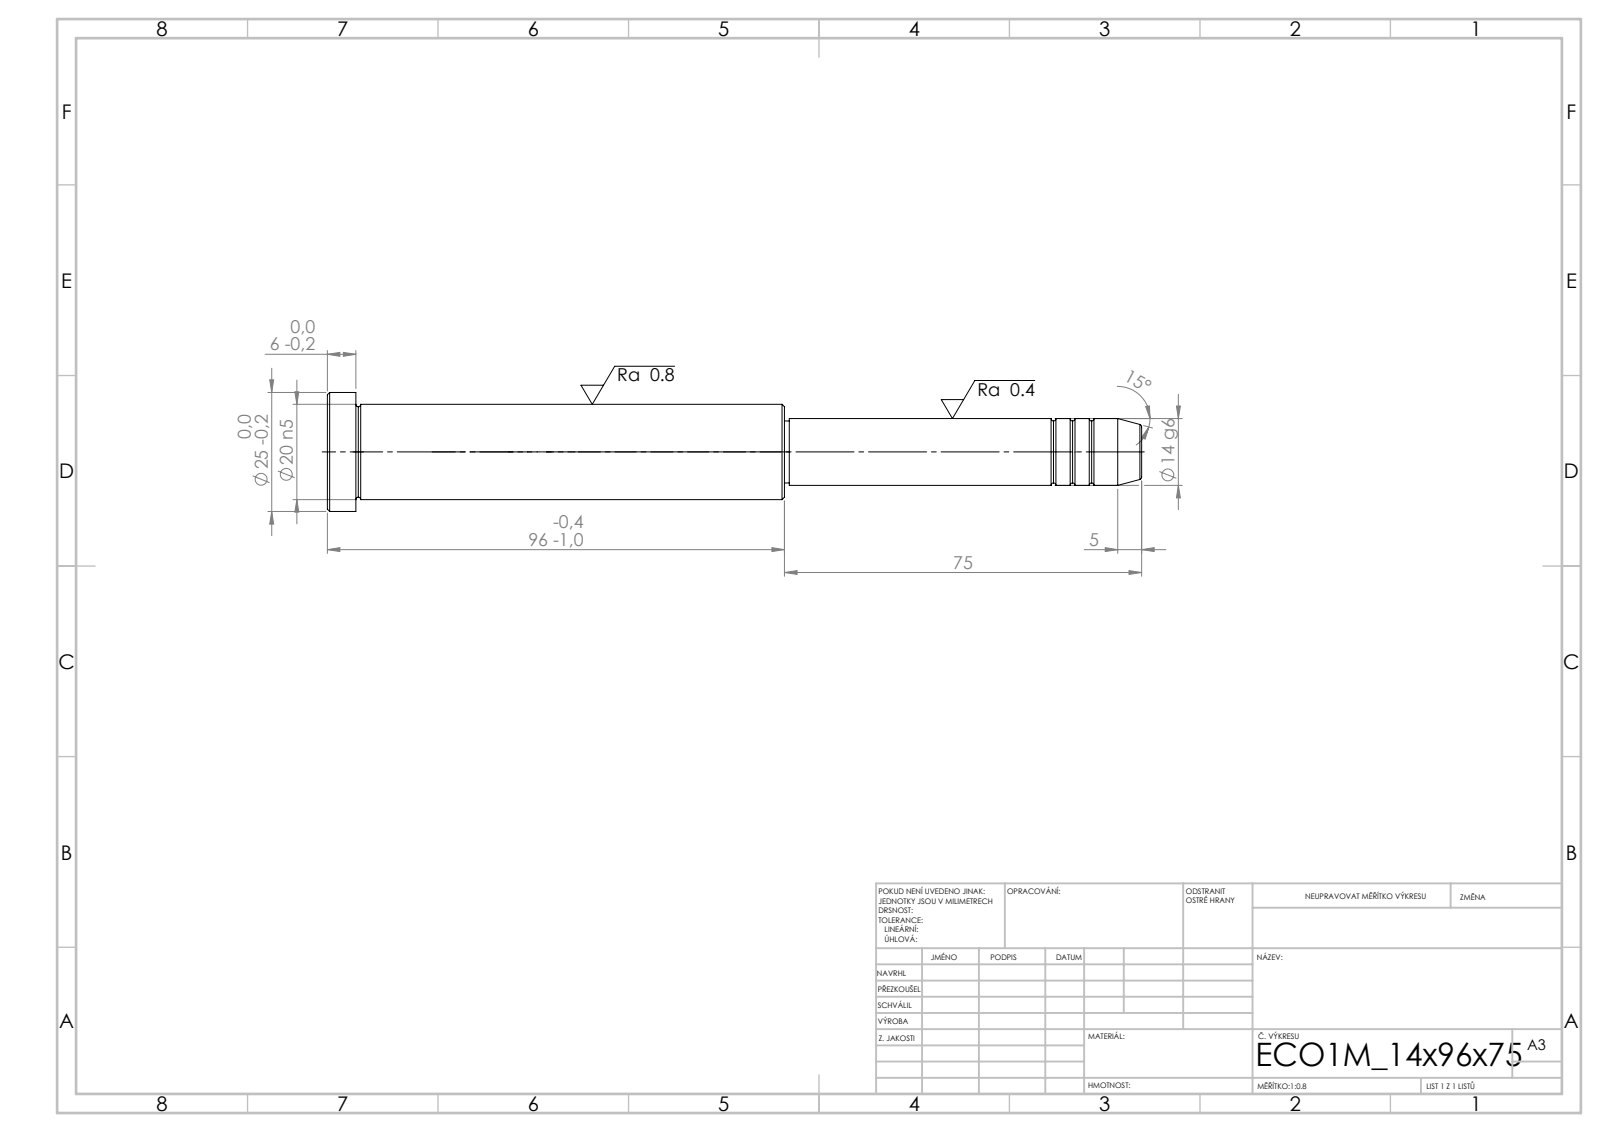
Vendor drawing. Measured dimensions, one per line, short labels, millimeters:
written by: SolidWorks 2019 (CONFIG_CONTROL_DESIGN)
unit: mm
bodies: 1 solid, 43 faces (5 planar, 14 cylindrical, 24 other)
size: 171 × 25 × 25
volume: 42 513 mm³; area: 10 431 mm²
bosses: 1× ⌀25, 1× ⌀20, 1× ⌀14, 1× ⌀13
face distances: 6, 90, 96, 75, 165, 171, 74, 1, 91, 97
